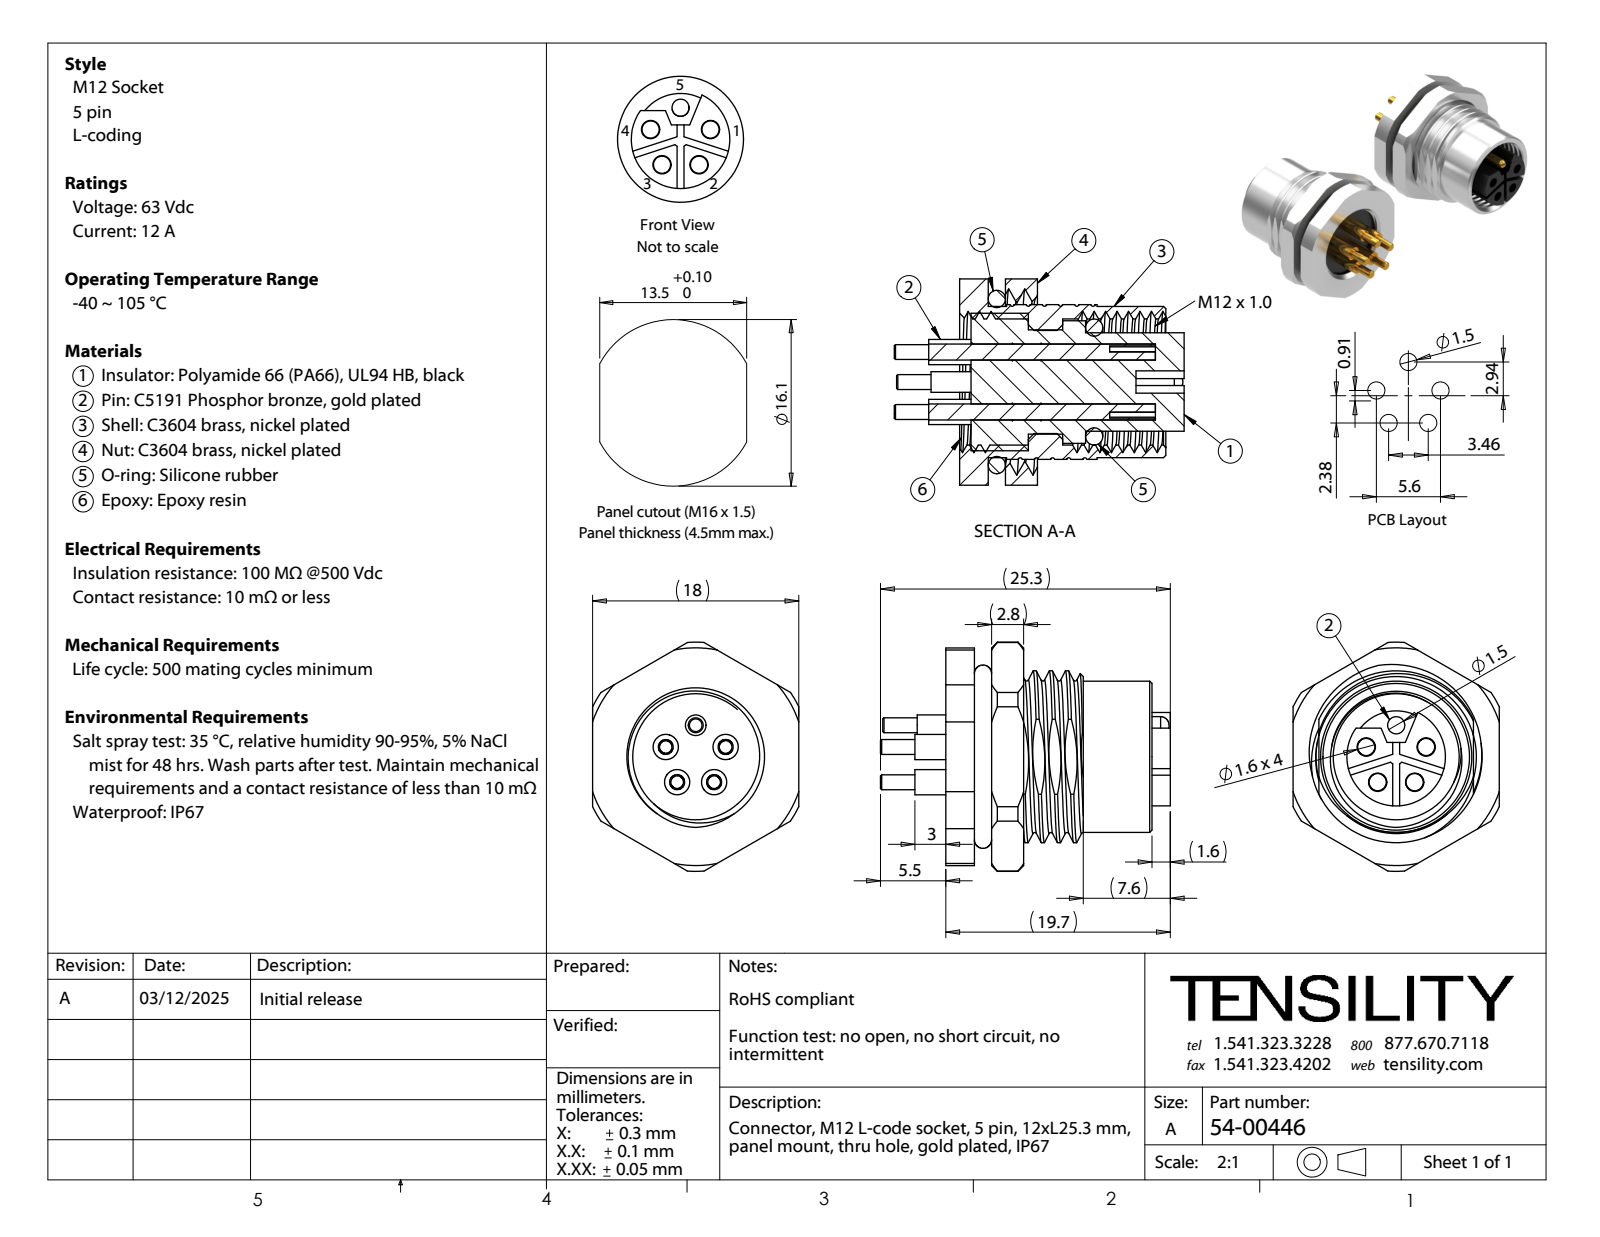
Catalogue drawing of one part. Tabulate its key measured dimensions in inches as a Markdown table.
| quantity | value |
| --- | --- |
| part name | 54-00446-02; 54-00446-05; 54-00446; 54-00446-07 (+4 more) |
| STEP written by | SolidWorks 2021 (CONFIG_CONTROL_DESIGN) |
| units | inches |
| bodies | 10 solids, 353 faces (119 planar, 137 cylindrical, 97 other) |
| overall size | 0.996 × 0.78 × 0.765 |
| volume | 0.181 in³ |
| surface area | 8.821 in² |
| round holes (diameter × count) | 0.059 × 5, 0.063 × 4, 0.354 × 1, 0.433 × 1, 0.551 × 1 |
| round bosses / shafts (diameter × count) | 0.051 × 5, 0.087 × 4, 0.52 × 1, 0.472 × 1, 0.421 × 1, 0.358 × 1, 0.339 × 1, 0.071 × 1 |
| partial cylindrical surfaces (radius × count) | 0.295 × 1, 0.374 × 1, 0.394 × 1 |
| main face-to-face distances | 0.059, 0.098, 0.118, 0.197, 0.709, 0.039, 0.268, 0.079, 0.157, 0.236 |
| hole center spacings | 0.108, 0.206, 0.128, 0.127, 0.206 |
